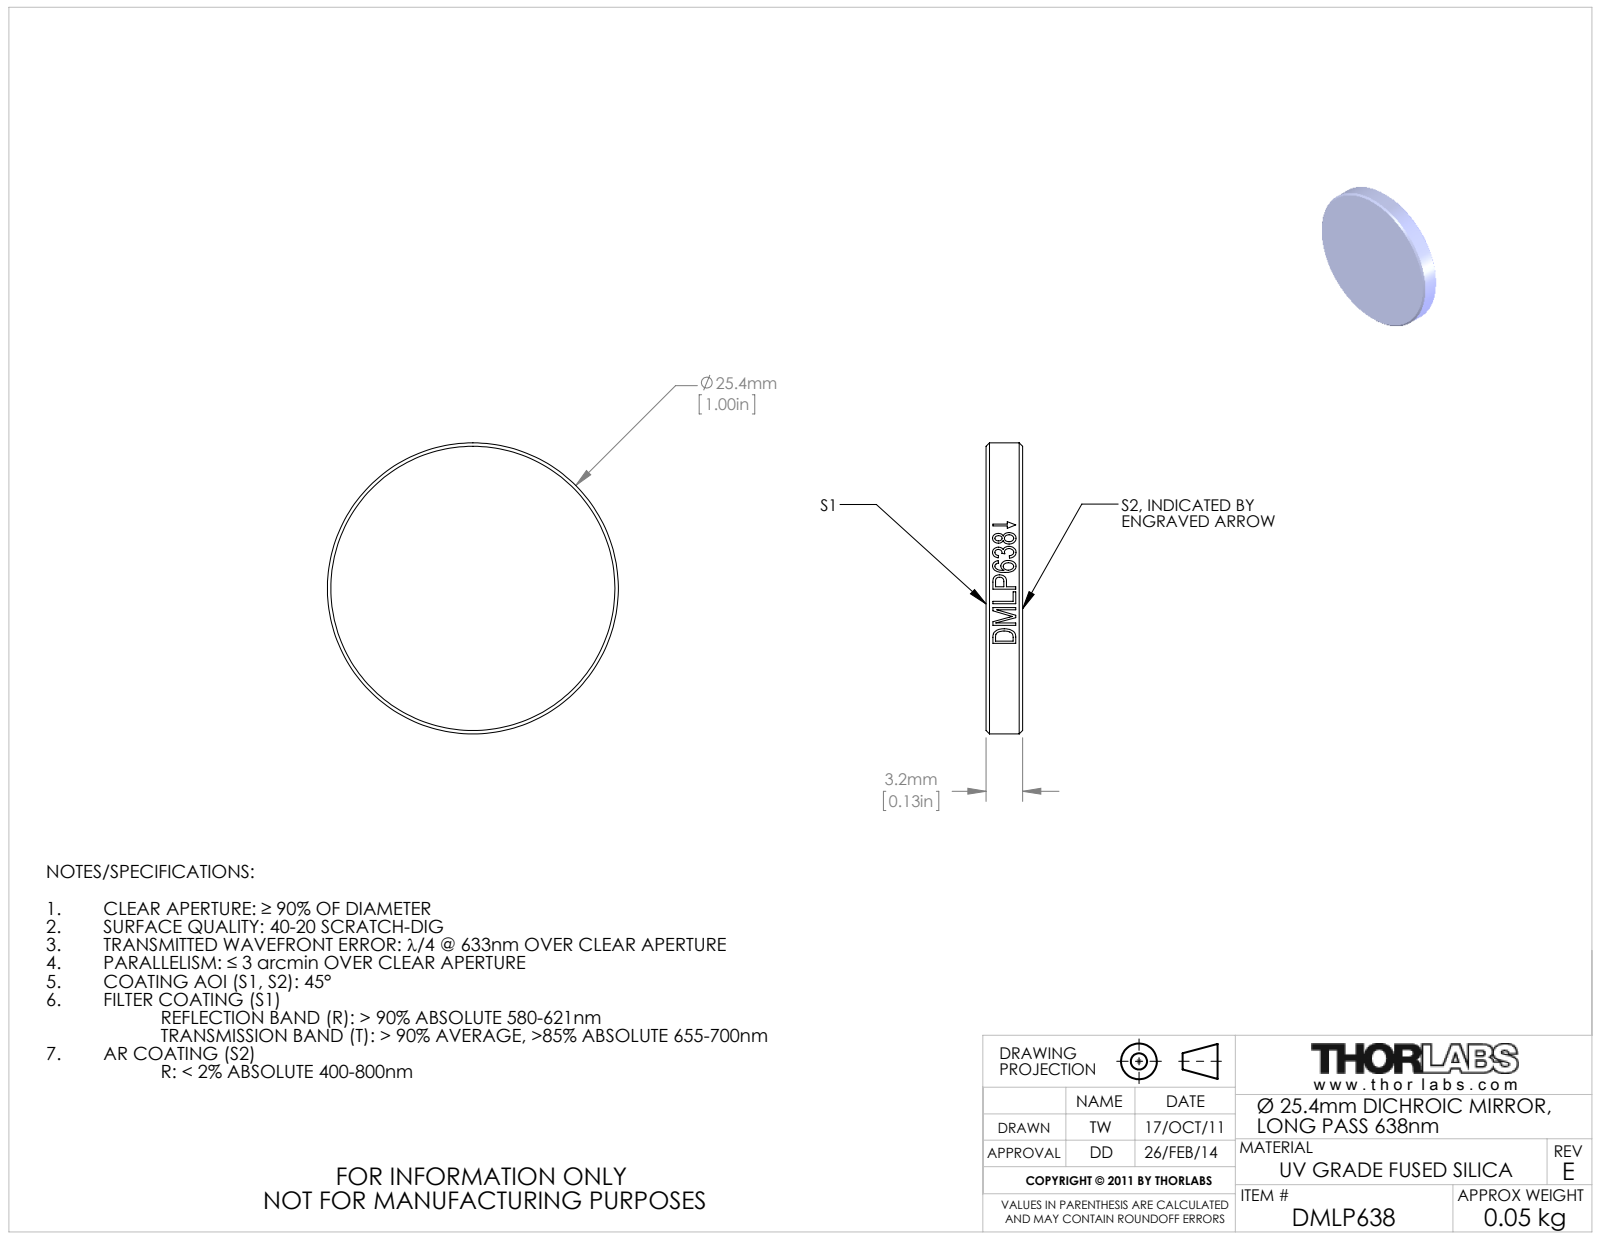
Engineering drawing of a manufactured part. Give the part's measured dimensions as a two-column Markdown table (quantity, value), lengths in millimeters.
| quantity | value |
| --- | --- |
| part name | 18098-E0W |
| STEP written by | SolidWorks 2011 (CONFIG_CONTROL_DESIGN) |
| units | millimeters |
| bodies | 0 solids, 21 faces (2 planar, 15 cylindrical, 4 other) |
| overall size | 25.4 × 25.4 × 3.2 |
| round bosses / shafts (diameter × count) | 25.4 × 1 |
| main face-to-face distances | 3.2 |
